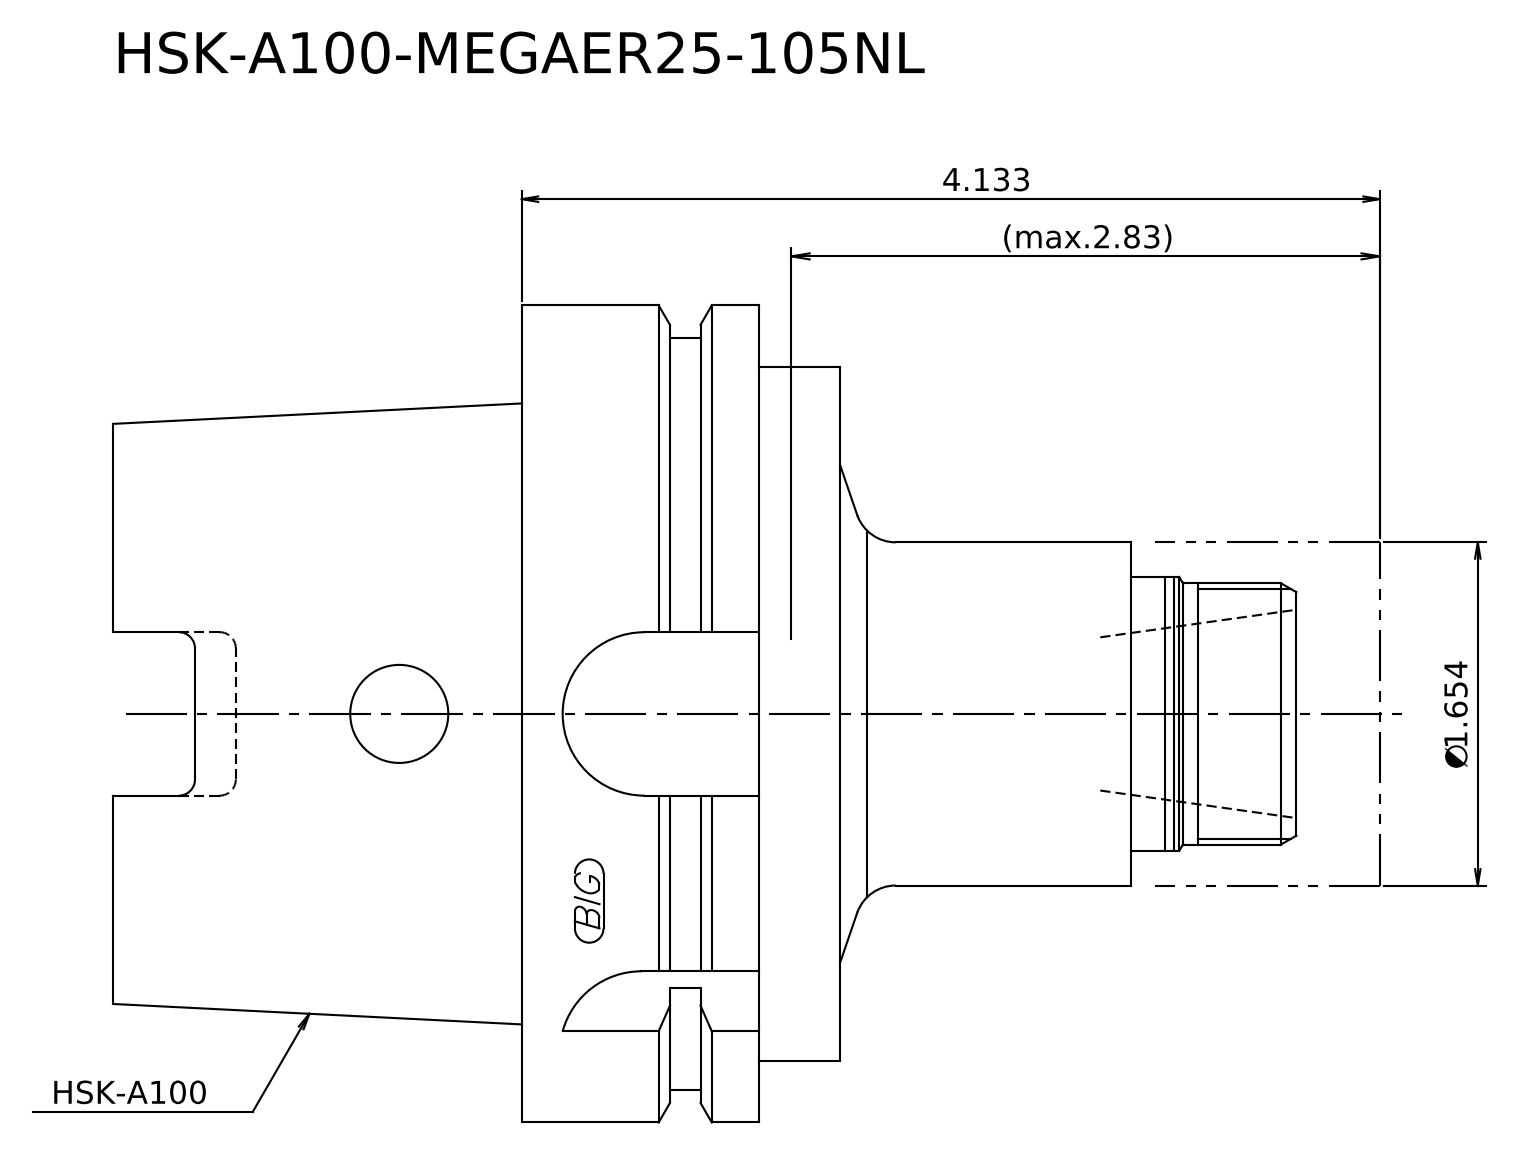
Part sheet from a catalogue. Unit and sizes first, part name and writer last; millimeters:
Units: millimetres
Overall size (bounding box): 155 × 100 × 100
Round bosses / shafts (diameter × count): ⌀100 ×1, ⌀92 ×1, ⌀85 ×1, ⌀42 ×1, ⌀33.5 ×1, ⌀32 ×1
Main face-to-face distances: 50, 39, 89, 10, 29, 79, 38.5, 48.5, 77.5, 127.5
Volume: 599 972 mm³ · Surface area: 52 641 mm²
Bodies: 2 solids, 24 faces (10 planar, 8 cylindrical, 6 other)
STEP written by: Kubotek KeyCreator 2011 V10.0.2 (22737) (automotive_design)
